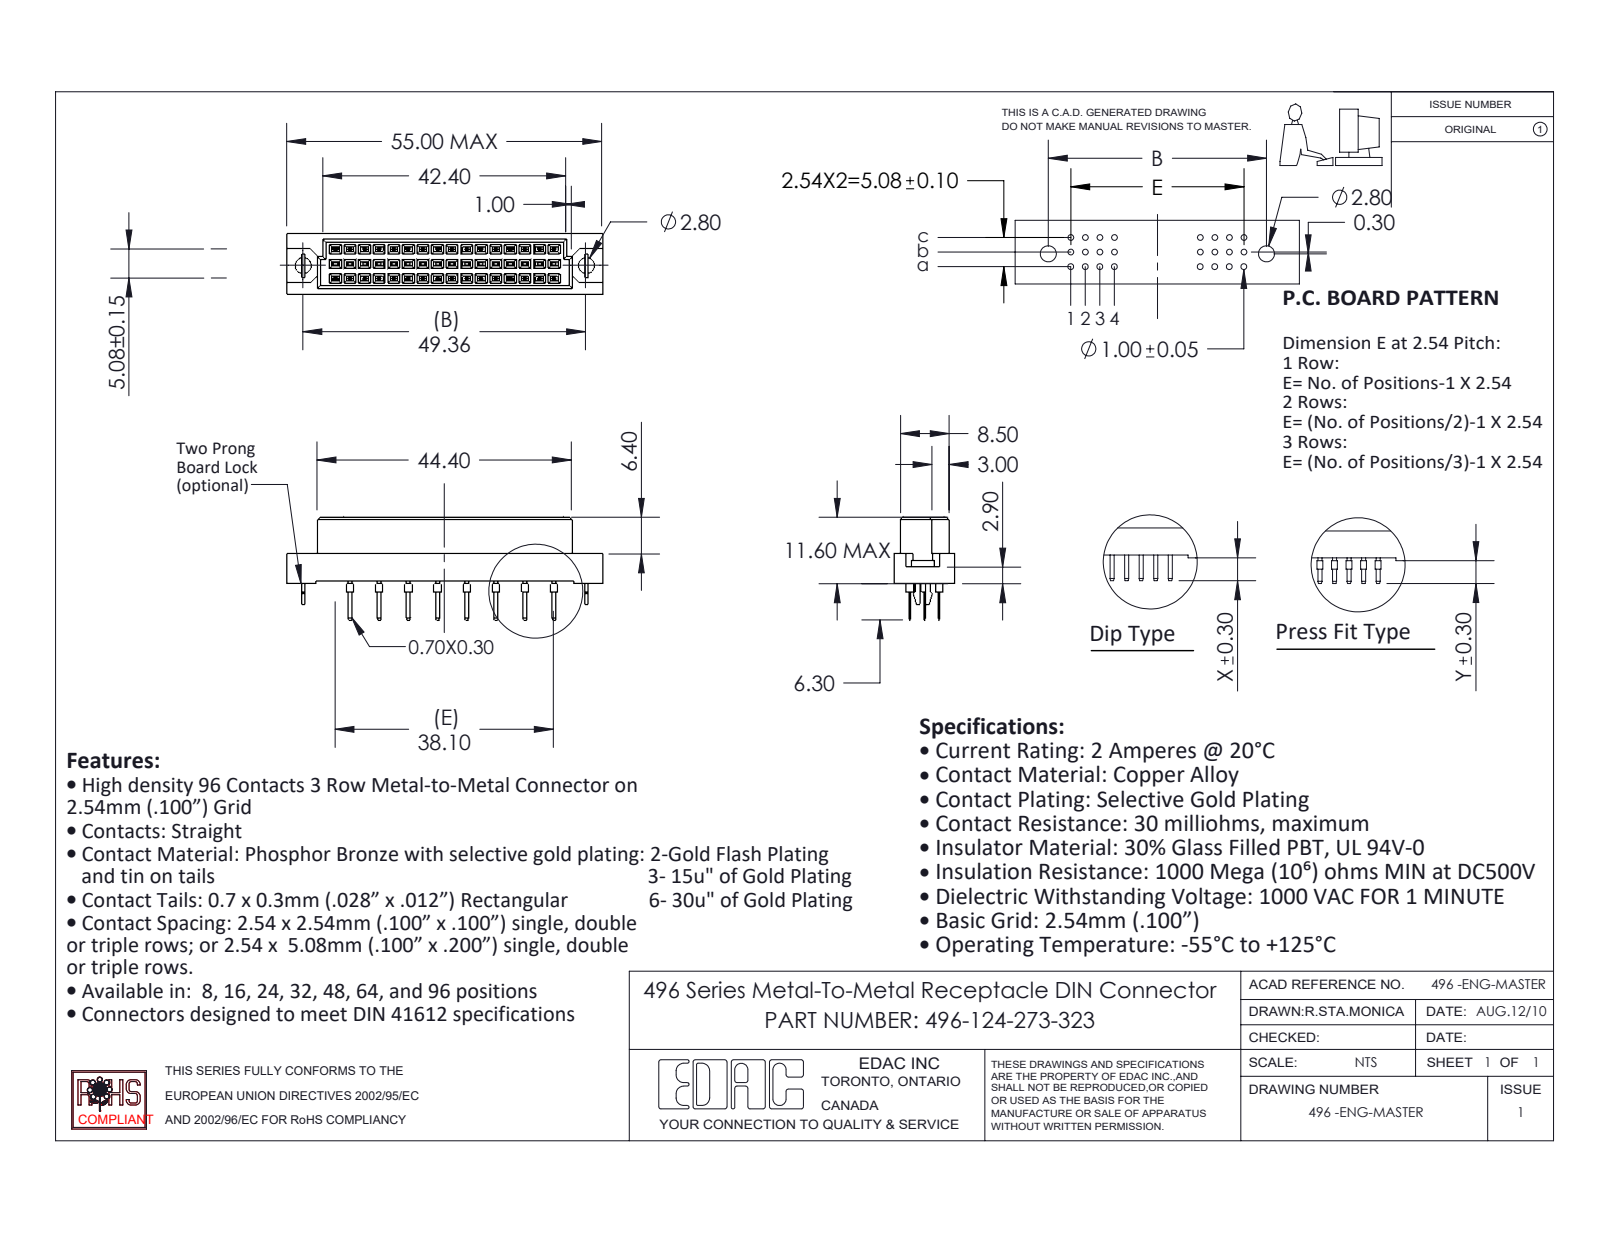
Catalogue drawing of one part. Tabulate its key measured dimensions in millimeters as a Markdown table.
| quantity | value |
| --- | --- |
| part name | 496 Part_48; 496 Bore-lock; 496-290_73; 496-124-273-323 |
| STEP written by | SolidWorks 2020 (CONFIG_CONTROL_DESIGN) |
| units | millimeters |
| bodies | 27 solids, 1134 faces (1080 planar, 54 cylindrical, 0 other) |
| overall size | 55 × 17.9 × 10.6 |
| volume | 4 686 mm³ |
| surface area | 4 911 mm² |
| round holes (diameter × count) | 2.8 × 2 |
| round bosses / shafts (diameter × count) | 1 × 24 |
| partial cylindrical surfaces (radius × count) | 0.53 × 1 |
| main face-to-face distances | 2.54, 5.08, 1.05, 9.55, 0.81, 0.56, 0.55, 10.6, 3.35, 1.73 |
| hole center spacings | 49.36 |
